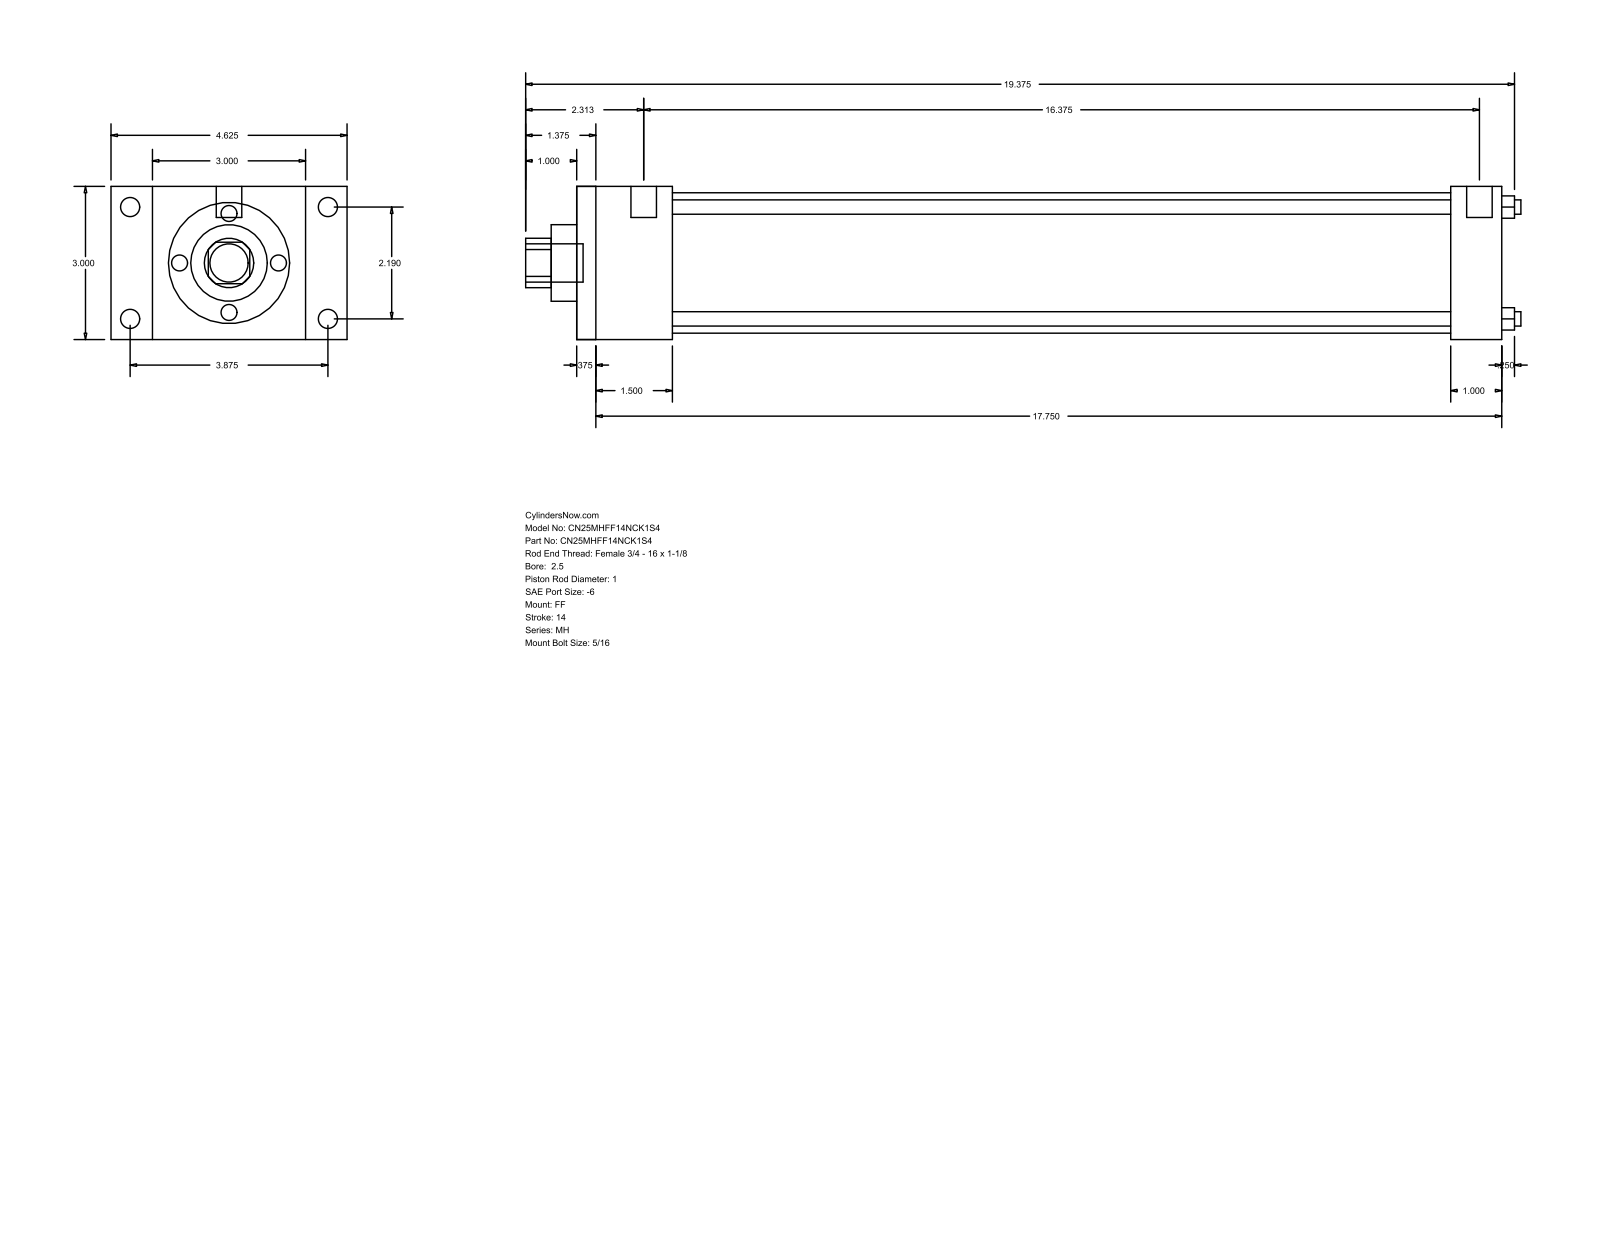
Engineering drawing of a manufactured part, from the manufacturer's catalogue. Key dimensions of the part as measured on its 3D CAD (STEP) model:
Part name (STEP PRODUCT): MH_FF__0250_1
STEP written by: GSSL Pune (CONFIG_CONTROL_DESIGN)
Units: millimetres
Bodies: 0 solids, 92 faces (64 planar, 28 cylindrical, 0 other)
Overall size (bounding box): 495.3 × 117.47 × 76.2
Round holes (diameter × count): ⌀7.14 ×4, ⌀25.4 ×1, ⌀38.1 ×1, ⌀69.85 ×1
Round bosses / shafts (diameter × count): ⌀9.53 ×4, ⌀5.56 ×4, ⌀12.7 ×2, ⌀19.05 ×1
Partial cylindrical surfaces — rounded edges, fillets, slot ends (radius × count): R12.29 ×1
Main face-to-face distances: 76.2, 460.37, 450.85, 9.52, 25.39, 47.63, 434.98, 38.11, 425.46, 387.35
Hole centre spacings: 39.33, 55.62, 78.66
